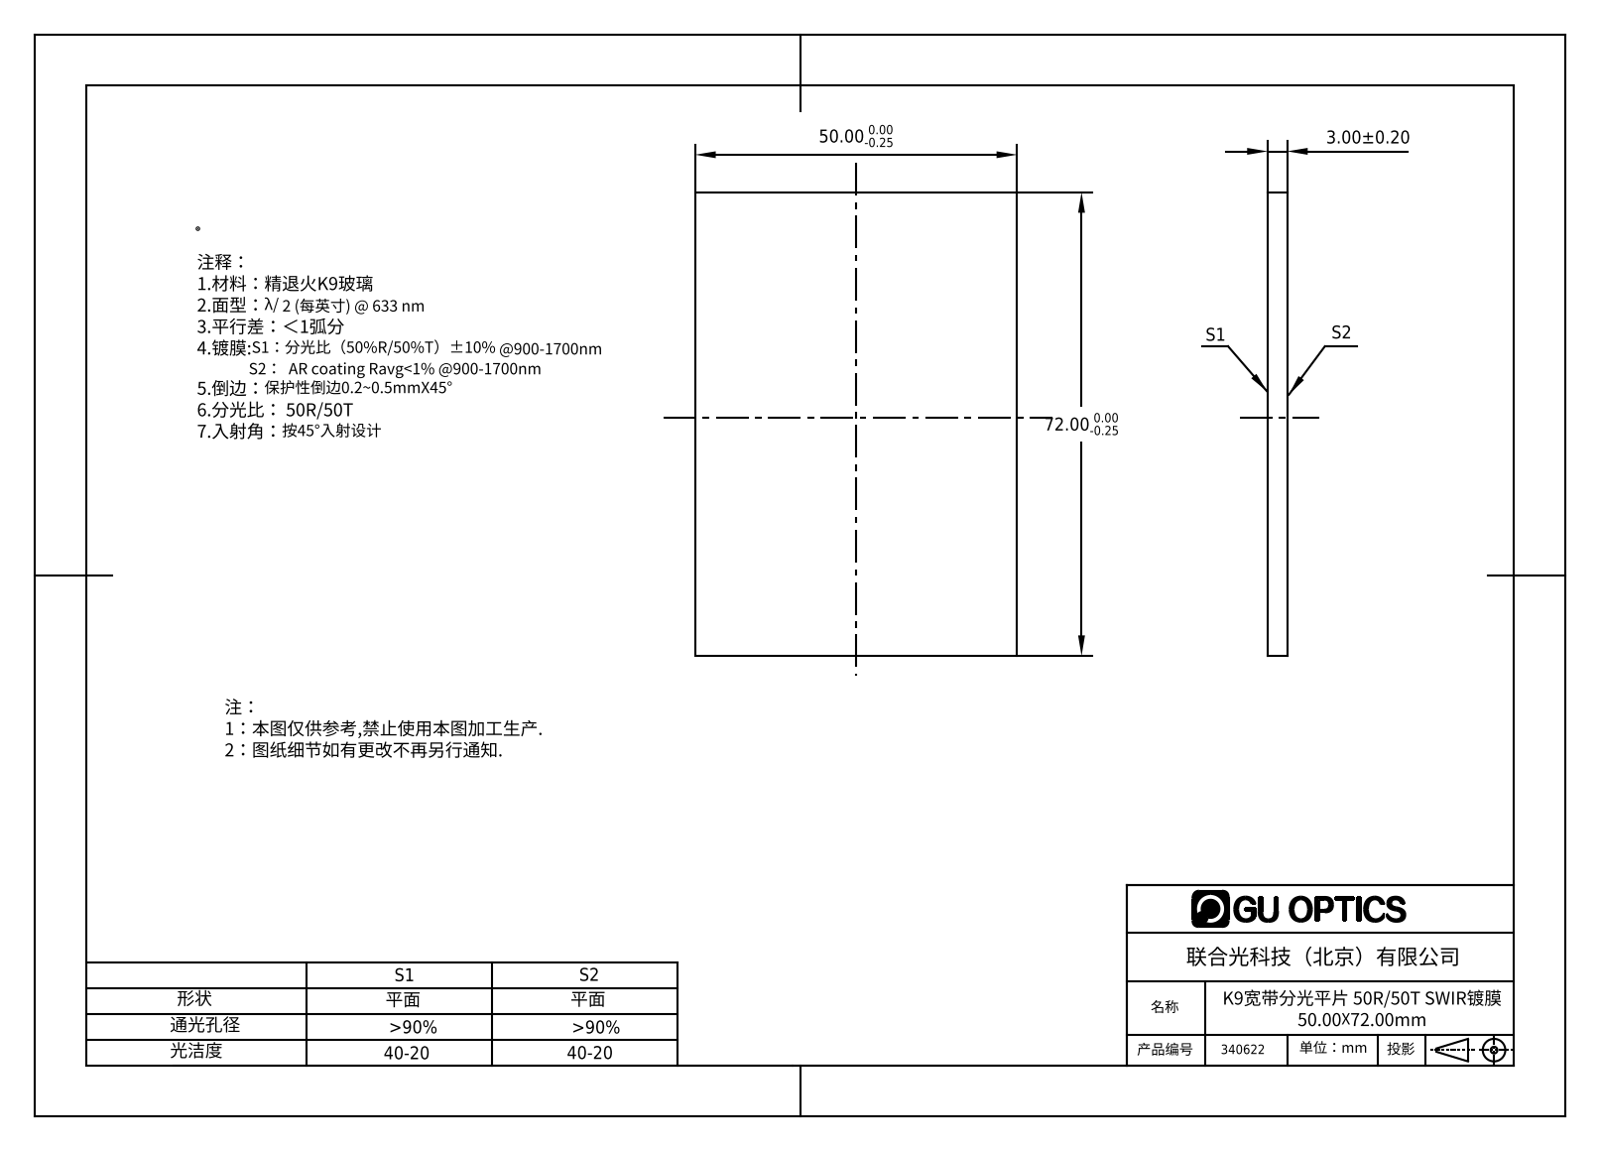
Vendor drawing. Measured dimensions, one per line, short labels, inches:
name: 340535
written by: SolidWorks 2016 (CONFIG_CONTROL_DESIGN)
unit: in
bodies: 1 solid, 6 faces (6 planar, 0 cylindrical, 0 other)
size: 2.835 × 1.969 × 0.118
volume: 0.659 in³; area: 12.29 in²
face distances: 0.118, 1.969, 2.835
